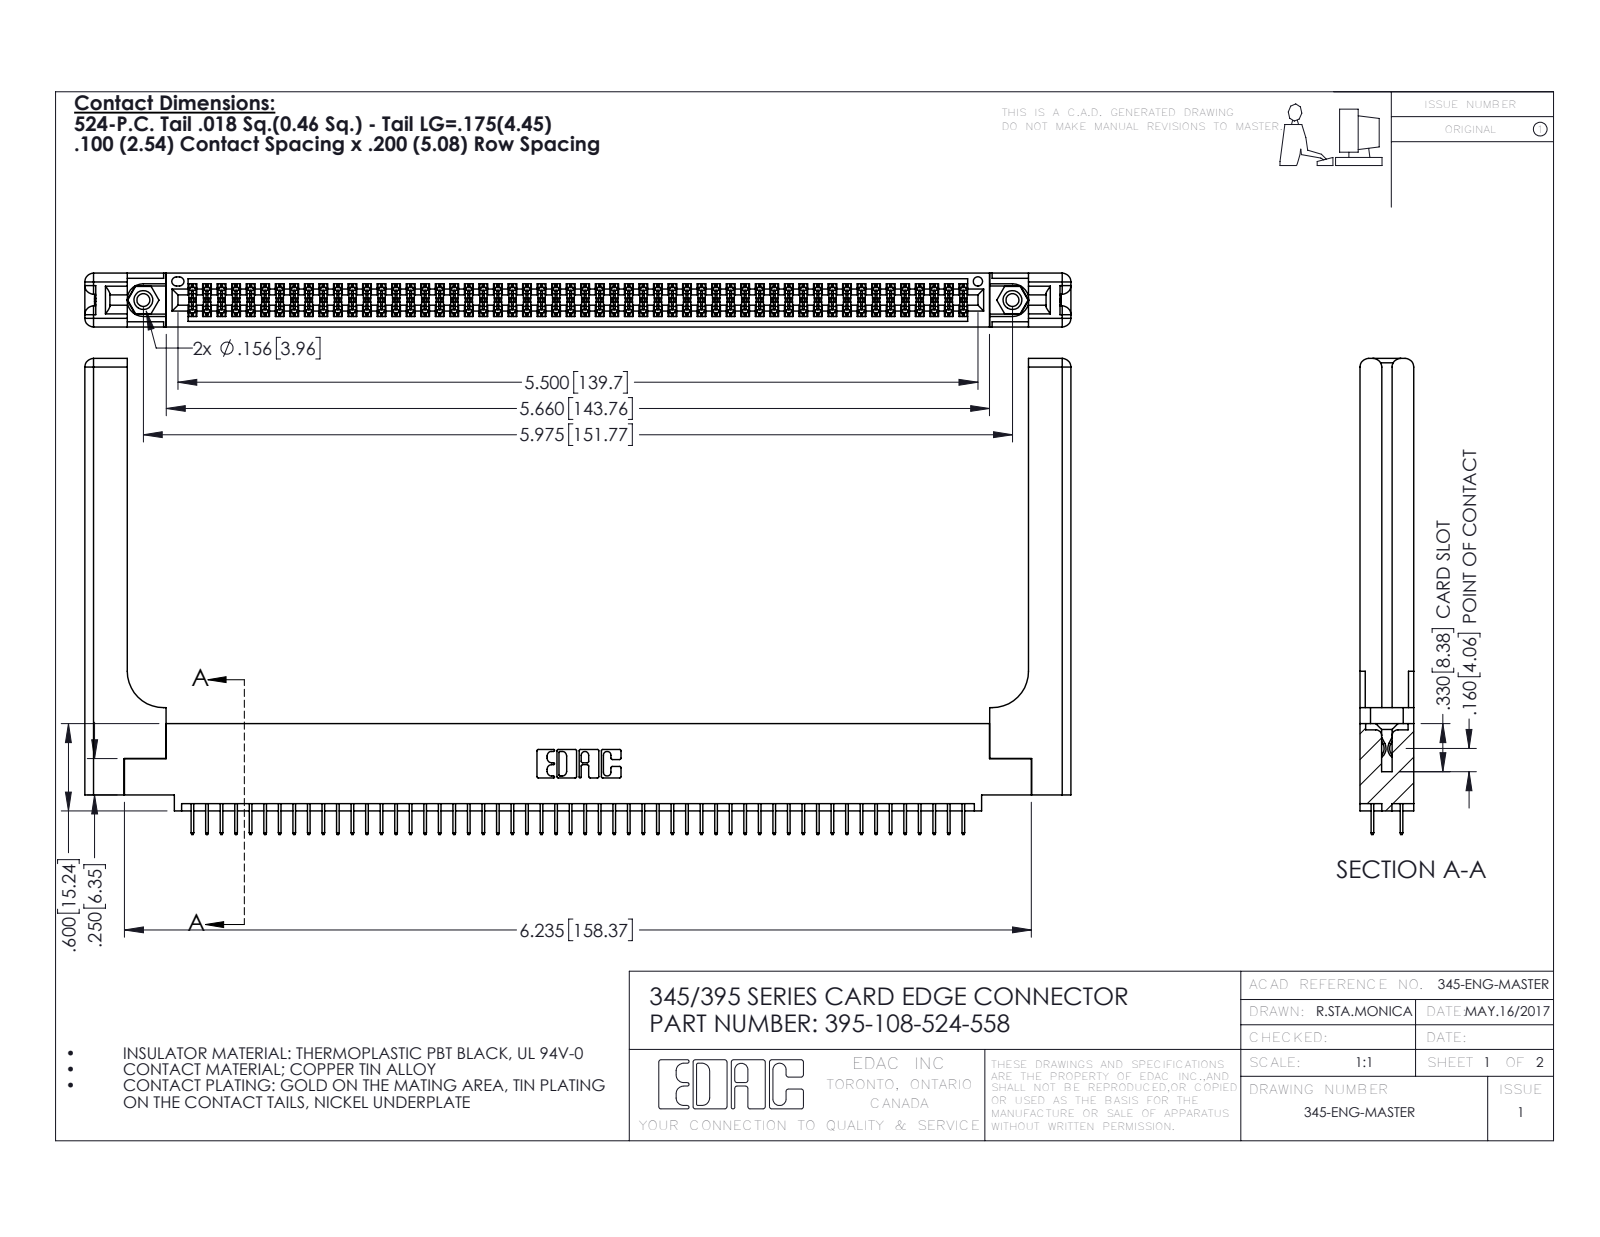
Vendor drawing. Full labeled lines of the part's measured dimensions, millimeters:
Part name (STEP PRODUCT): 345-250-001_345-250-001-102; 345 Part_0.110 Offset - 0.156 Dia-TH; 395-108-524-558; 345-292-001_345-293-124 (+1 more)
STEP written by: SolidWorks 2016 (CONFIG_CONTROL_DESIGN)
Units: millimetres
Bodies: 113 solids, 6218 faces (4444 planar, 1714 cylindrical, 60 other)
Overall size (bounding box): 172.2 × 83.1 × 9.4
Volume: 25 070 mm³ · Surface area: 29 490 mm²
Round holes (diameter × count): ⌀2.3 ×2, ⌀3.2 ×2, ⌀4 ×2, ⌀1.6 ×1
Round bosses / shafts (diameter × count): ⌀3.9 ×2
Partial cylindrical surfaces — rounded edges, fillets, slot ends (radius × count): R0.2 ×162, R0.3 ×22, R1.5 ×16, R0.2 ×6, R0.8 ×6, R0.7 ×3, R0.4 ×2, R0.5 ×2
Main face-to-face distances: 1.8, 9.4, 7.6, 5.1, 2.5, 6.9, 0.6, 5.7, 3.8, 3.8
Hole centre spacings: 6.9, 145.8, 151.8
